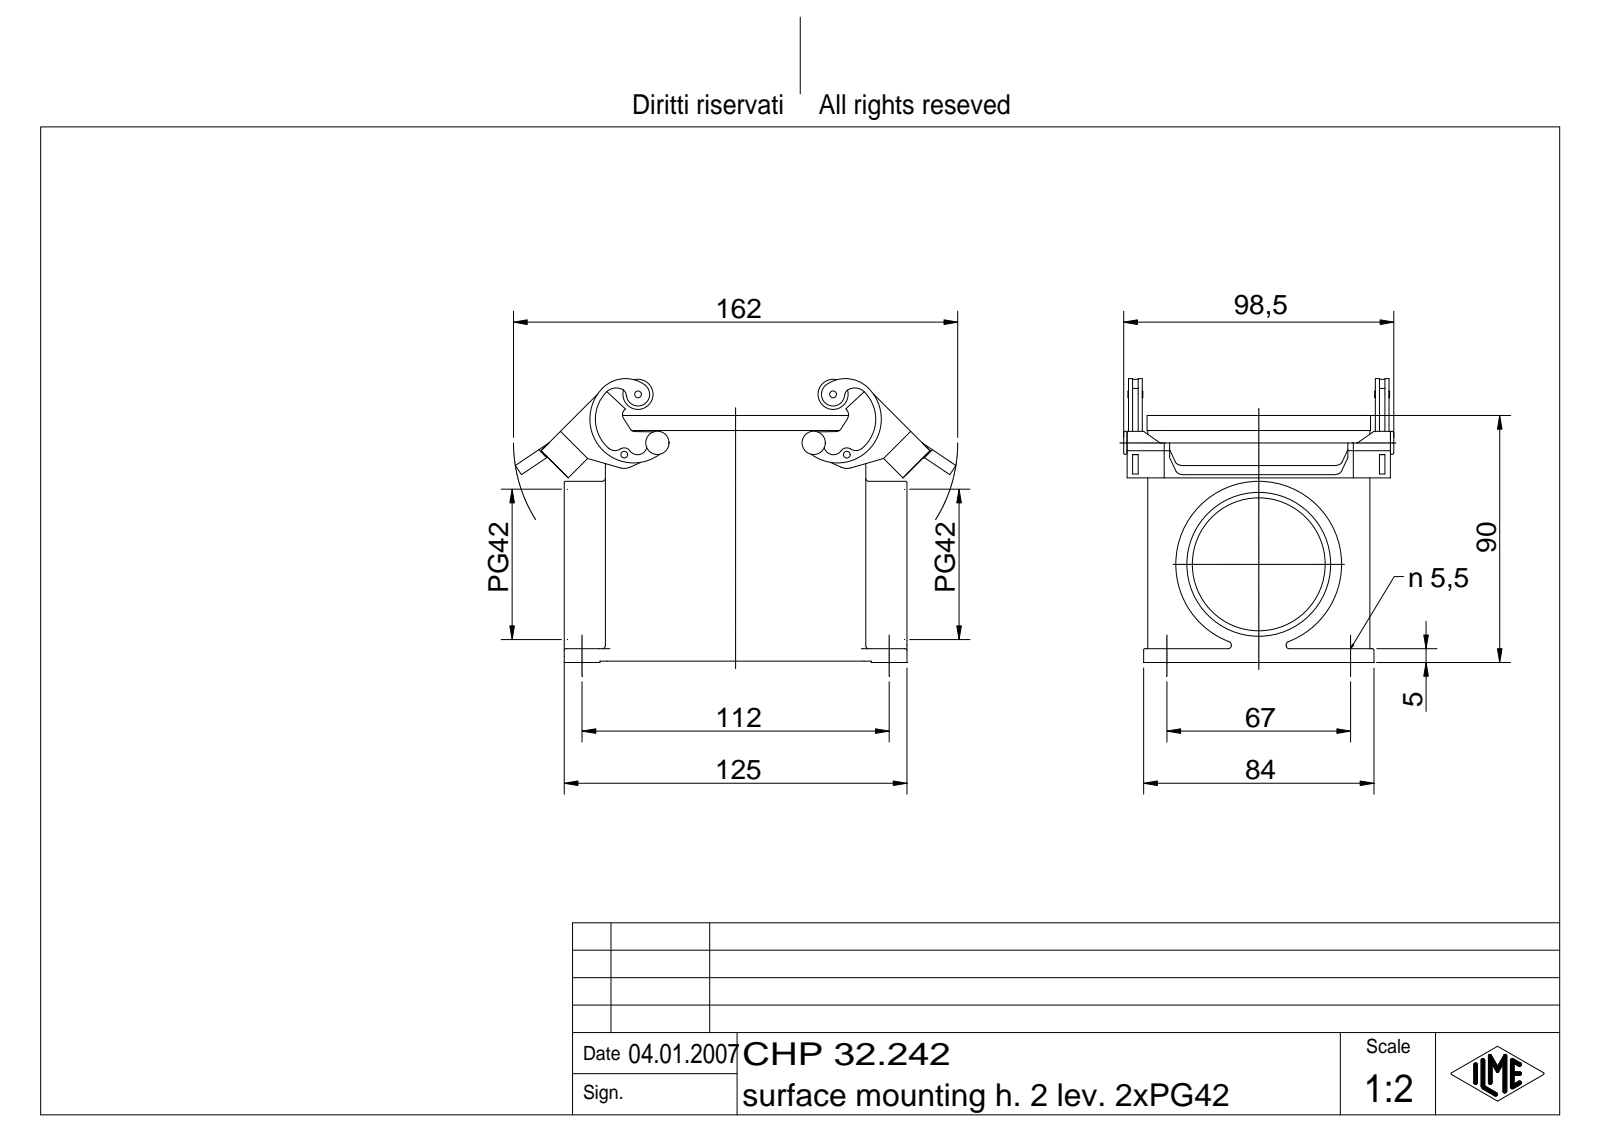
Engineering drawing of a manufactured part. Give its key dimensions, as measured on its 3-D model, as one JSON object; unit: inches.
{"part_name": "CHP 32.242", "step_written_by": "Autodesk Inventor 7 (AUTOMOTIVE_DESIGN)", "units": "inches", "bodies": {"solids": 1, "faces": 817, "planar": 156, "cylindrical": 269, "other": 392}, "overall_size": [6.327, 4.072, 3.878], "volume_in3": 12.95, "surface_area_in2": 163.9, "round_holes": [[0.079, 4], [0.097, 4], [0.122, 4], [0.098, 2], [0.217, 2], [1.909, 1], [2.066, 1]], "round_bosses_or_shafts": [[0.433, 2], [0.197, 2], [0.118, 2], [2.382, 1]], "partial_cylinders_radius": [[0.039, 23], [0.02, 14], [0.059, 8], [0.118, 8], [0.236, 8], [0.098, 6], [0.079, 4], [0.138, 4]], "face_to_face_distances": [0.118, 3.071, 3.189, 0.177, 2.953, 0.157, 3.622, 3.543, 0.128, 3.74], "hole_center_spacings": [0.888, 1.063, 3.051, 3.121, 3.231, 0.684, 1.328, 1.643]}
